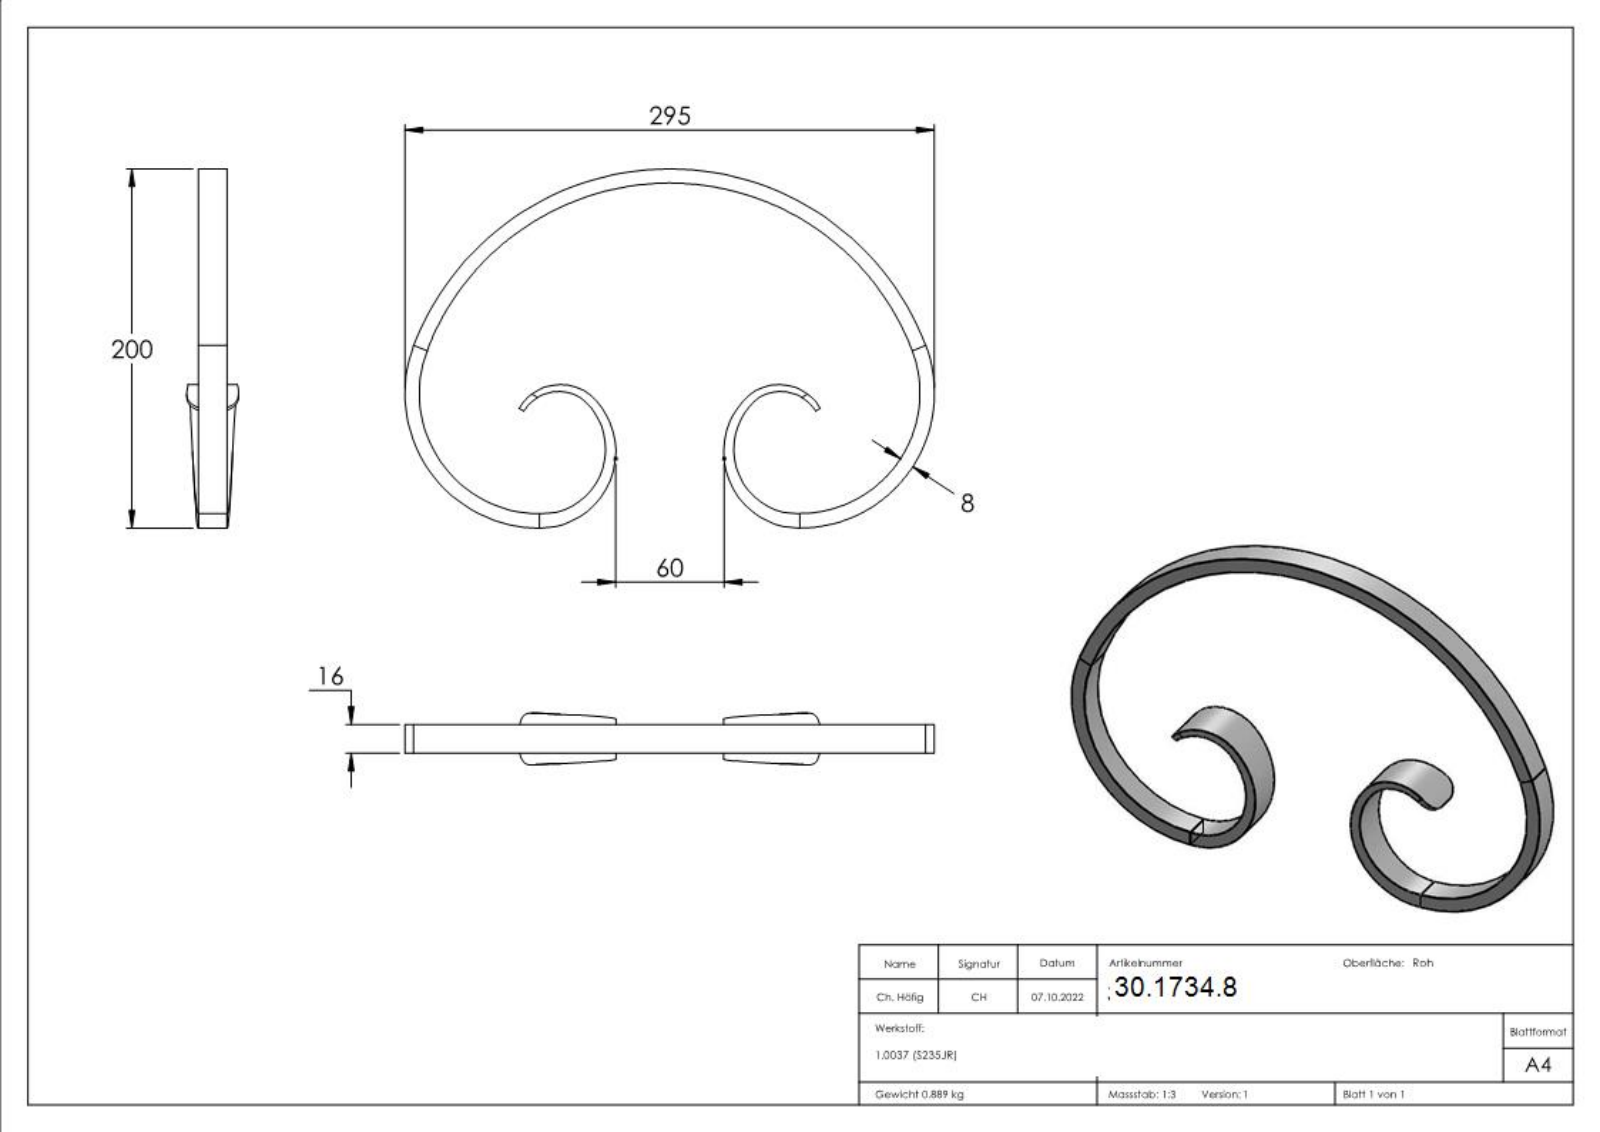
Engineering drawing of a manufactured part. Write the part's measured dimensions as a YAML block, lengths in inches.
part_name: "3084"
step_written_by: "SolidWorks 2018 (CONFIG_CONTROL_DESIGN)"
units: inches
bodies: {solids: 1, faces: 246, planar: 100, cylindrical: 26, other: 120}
overall_size: [11.614, 7.874, 1.143]
volume: 6.952
surface_area: 71.35
partial_cylinders:
  - {radius: 2.638, count: 2}
  - {radius: 2.953, count: 2}
  - {radius: 5.691, count: 1}
  - {radius: 5.695, count: 1}
  - {radius: 6.006, count: 1}
face_to_face_distances: [0.63, 0.124, 0.106, 0.087, 0.16, 0.013, 0.156, 0.315, 0.144, 0.013]
